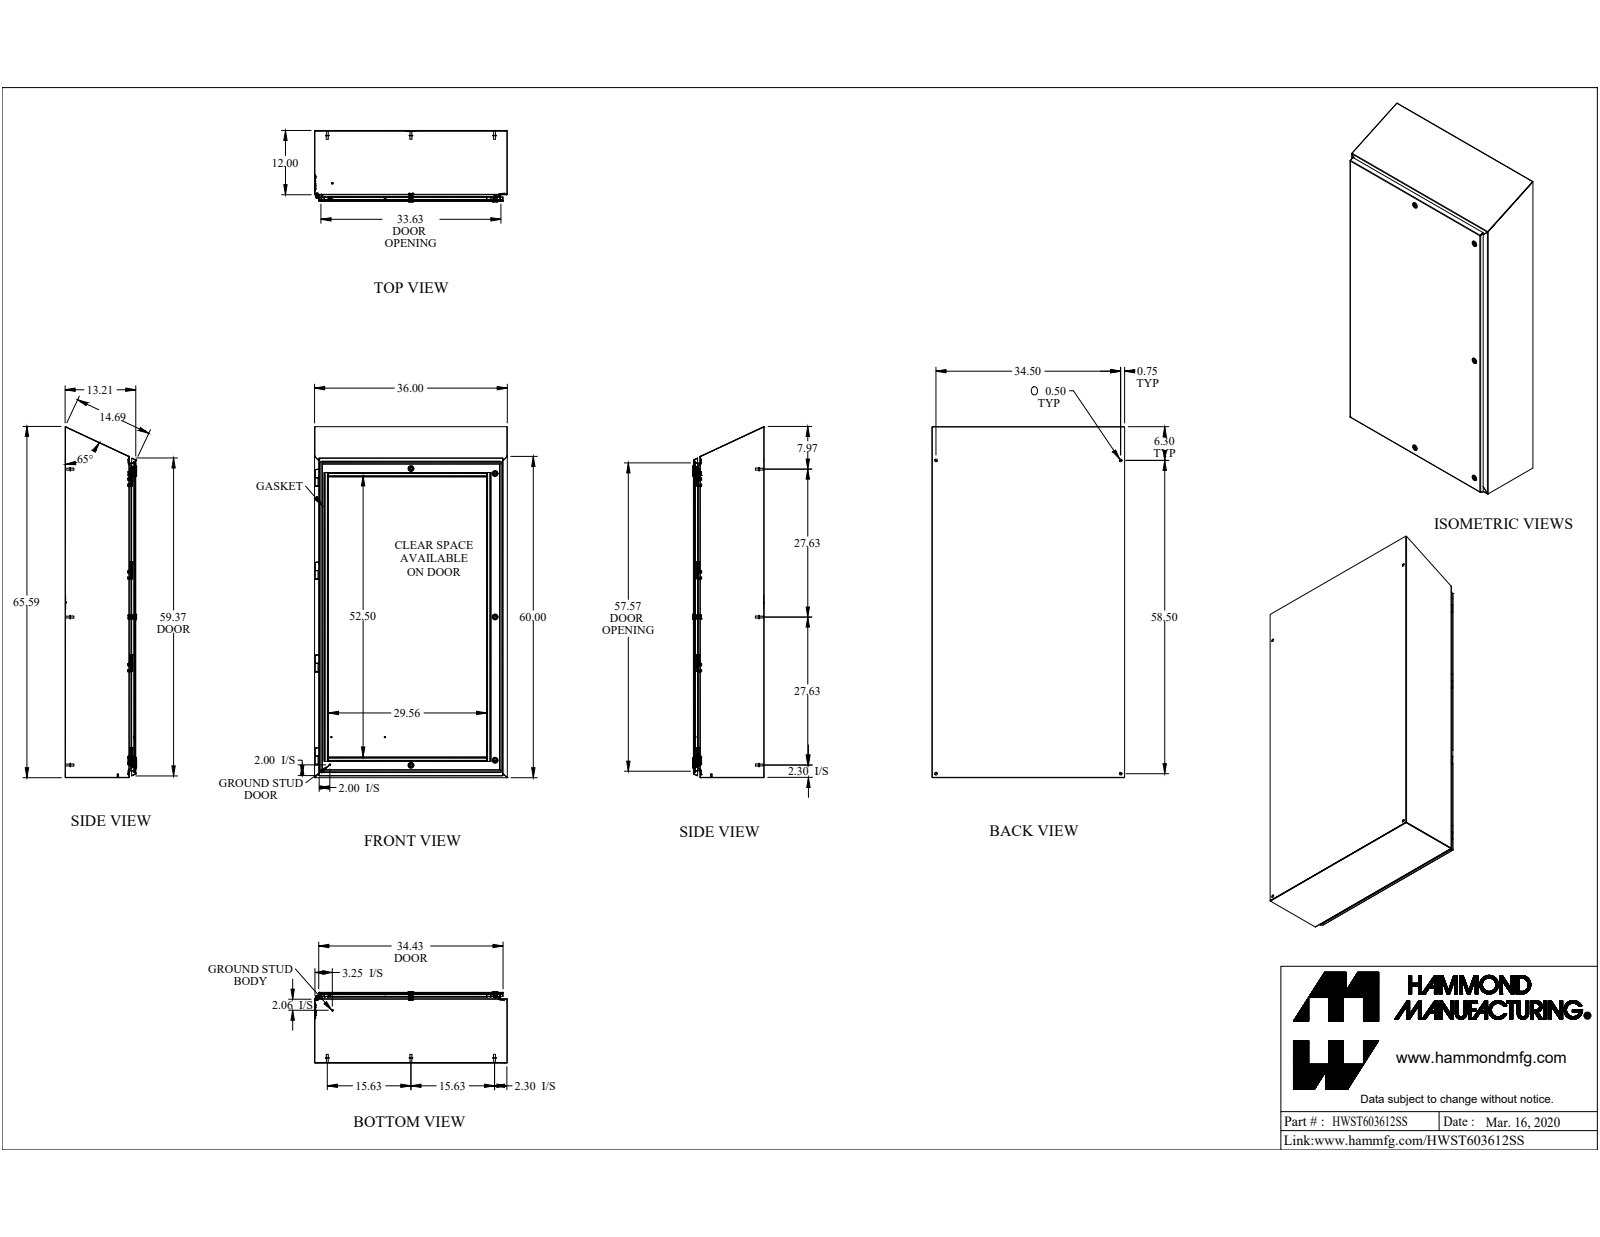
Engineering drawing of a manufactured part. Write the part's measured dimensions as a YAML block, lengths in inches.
part_name: "HWST603612SS"
step_written_by: "SolidWorks 2019 (AUTOMOTIVE_DESIGN)"
units: inches
bodies: {solids: 86, faces: 2051, planar: 1256, cylindrical: 559, other: 236}
overall_size: [65.545, 36, 13.37]
volume: 581.1
surface_area: 16373
round_holes:
  - {diameter: 0.194, count: 16}
  - {diameter: 0.24, count: 16}
  - {diameter: 0.5, count: 9}
  - {diameter: 0.275, count: 8}
  - {diameter: 0.197, count: 5}
  - {diameter: 0.387, count: 5}
  - {diameter: 0.63, count: 5}
  - {diameter: 0.768, count: 5}
  - {diameter: 0.13, count: 2}
  - {diameter: 0.24, count: 1}
  - {diameter: 3.5, count: 1}
round_bosses_or_shafts:
  - {diameter: 0.226, count: 16}
  - {diameter: 0.625, count: 11}
  - {diameter: 0.65, count: 8}
  - {diameter: 0.375, count: 8}
  - {diameter: 0.332, count: 8}
  - {diameter: 0.236, count: 6}
  - {diameter: 1.1, count: 5}
  - {diameter: 0.25, count: 4}
partial_cylinders:
  - {radius: 0.039, count: 32}
  - {radius: 0.125, count: 26}
  - {radius: 0.043, count: 24}
  - {radius: 0.25, count: 24}
  - {radius: 0.012, count: 20}
  - {radius: 0.036, count: 17}
  - {radius: 0.108, count: 17}
  - {radius: 0.03, count: 16}
face_to_face_distances: [0.072, 0.072, 13.066, 13.138, 13.138, 13.21, 35.856, 35.928, 35.928, 36]
hole_center_spacings: [1.142, 17.326, 17.324, 17.326, 17.324, 18.468, 34.648, 34.65]
